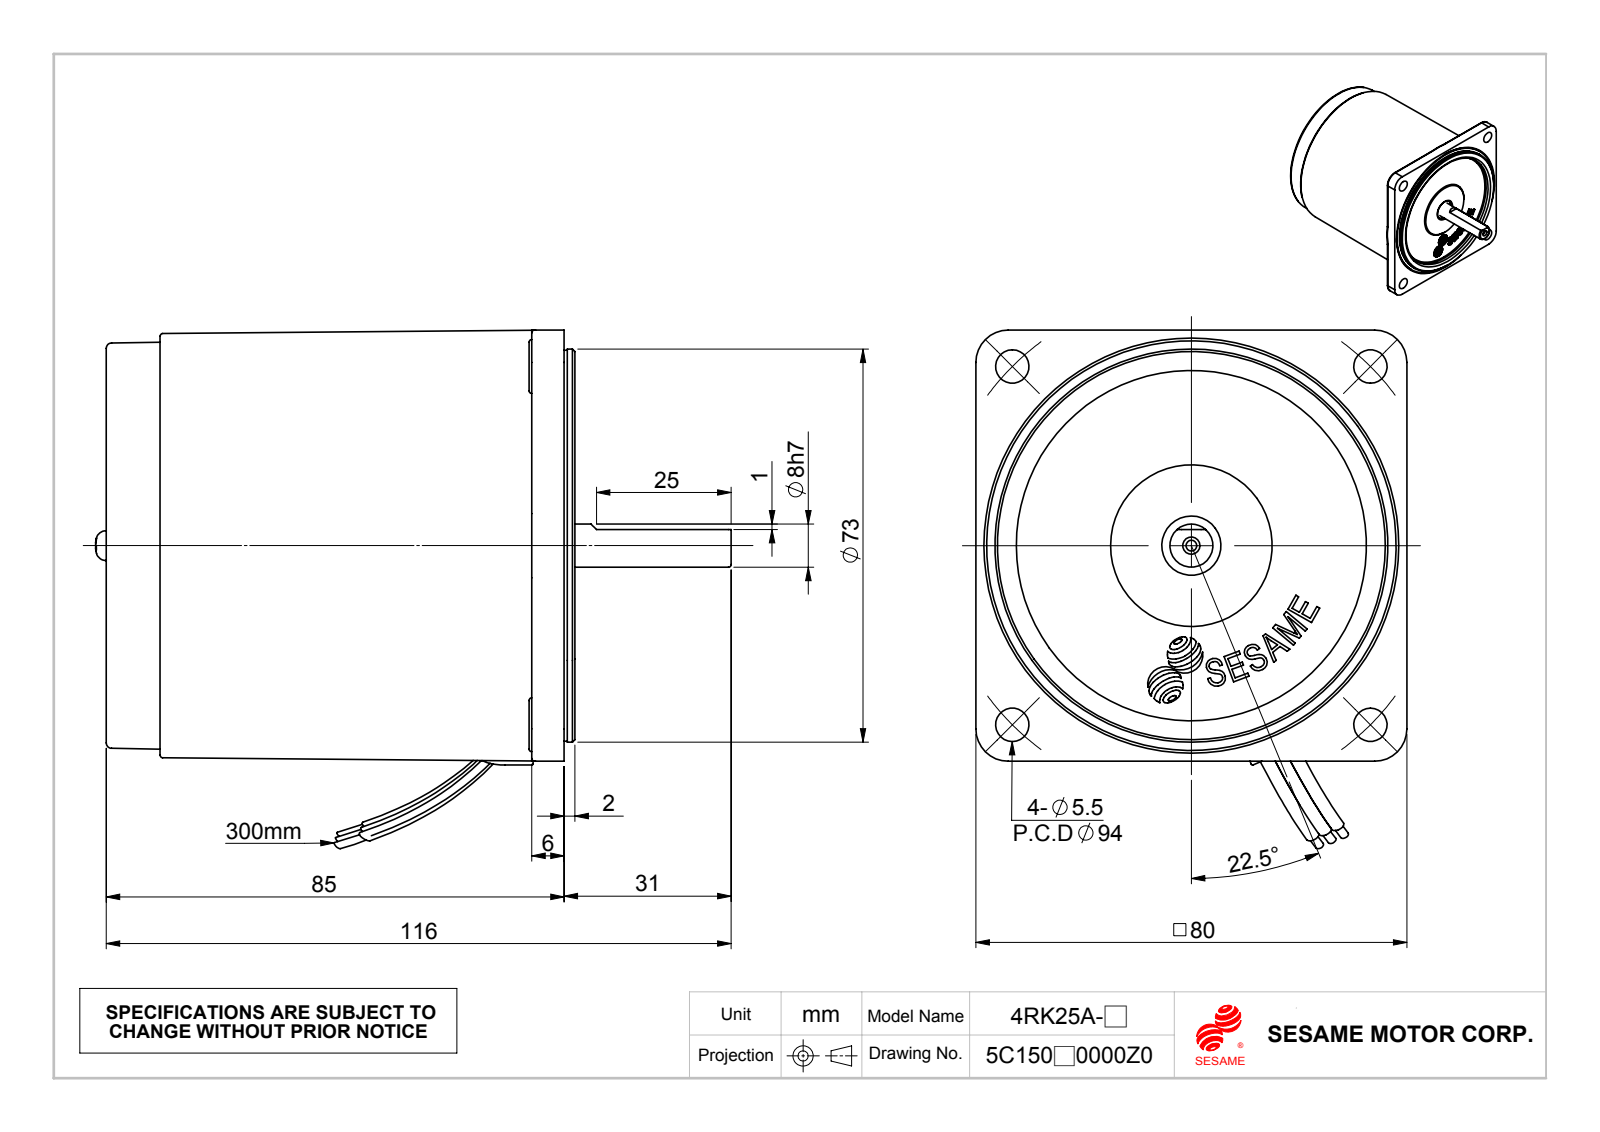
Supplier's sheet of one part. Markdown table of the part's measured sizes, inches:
| quantity | value |
| --- | --- |
| part name | 線扣; M425A-RK_成品; C475-C473_C475成品-車工; 25A_3.研磨 (+1 more) |
| STEP written by | SolidWorks 2010 (CONFIG_CONTROL_DESIGN) |
| units | inches |
| bodies | 10 solids, 520 faces (165 planar, 215 cylindrical, 140 other) |
| overall size | 4.644 × 3.788 × 3.15 |
| volume | 25.73 in³ |
| surface area | 77.72 in² |
| round holes (diameter × count) | 0.244 × 4, 0.098 × 3, 0.157 × 2, 0.079 × 1, 0.283 × 1, 0.374 × 1, 0.433 × 1, 2.362 × 1, 2.559 × 1, 2.992 × 1 |
| round bosses / shafts (diameter × count) | 0.217 × 2, 0.118 × 2, 2.871 × 1, 2.856 × 1, 1.575 × 1, 0.366 × 1, 0.315 × 1 |
| partial cylindrical surfaces (radius × count) | 0.01 × 8, 0.012 × 8, 0.024 × 8, 0.046 × 8, 0.051 × 8, 0.089 × 8, 0.006 × 4, 0.018 × 4 |
| main face-to-face distances | 0.039, 3.307, 3.244, 3.248, 0.02, 3.287, 3.283, 3.268, 0.024, 0.059 |
| hole center spacings | 1.492, 1.85, 2.306, 2.617, 0.591, 3.7, 1.181 |
